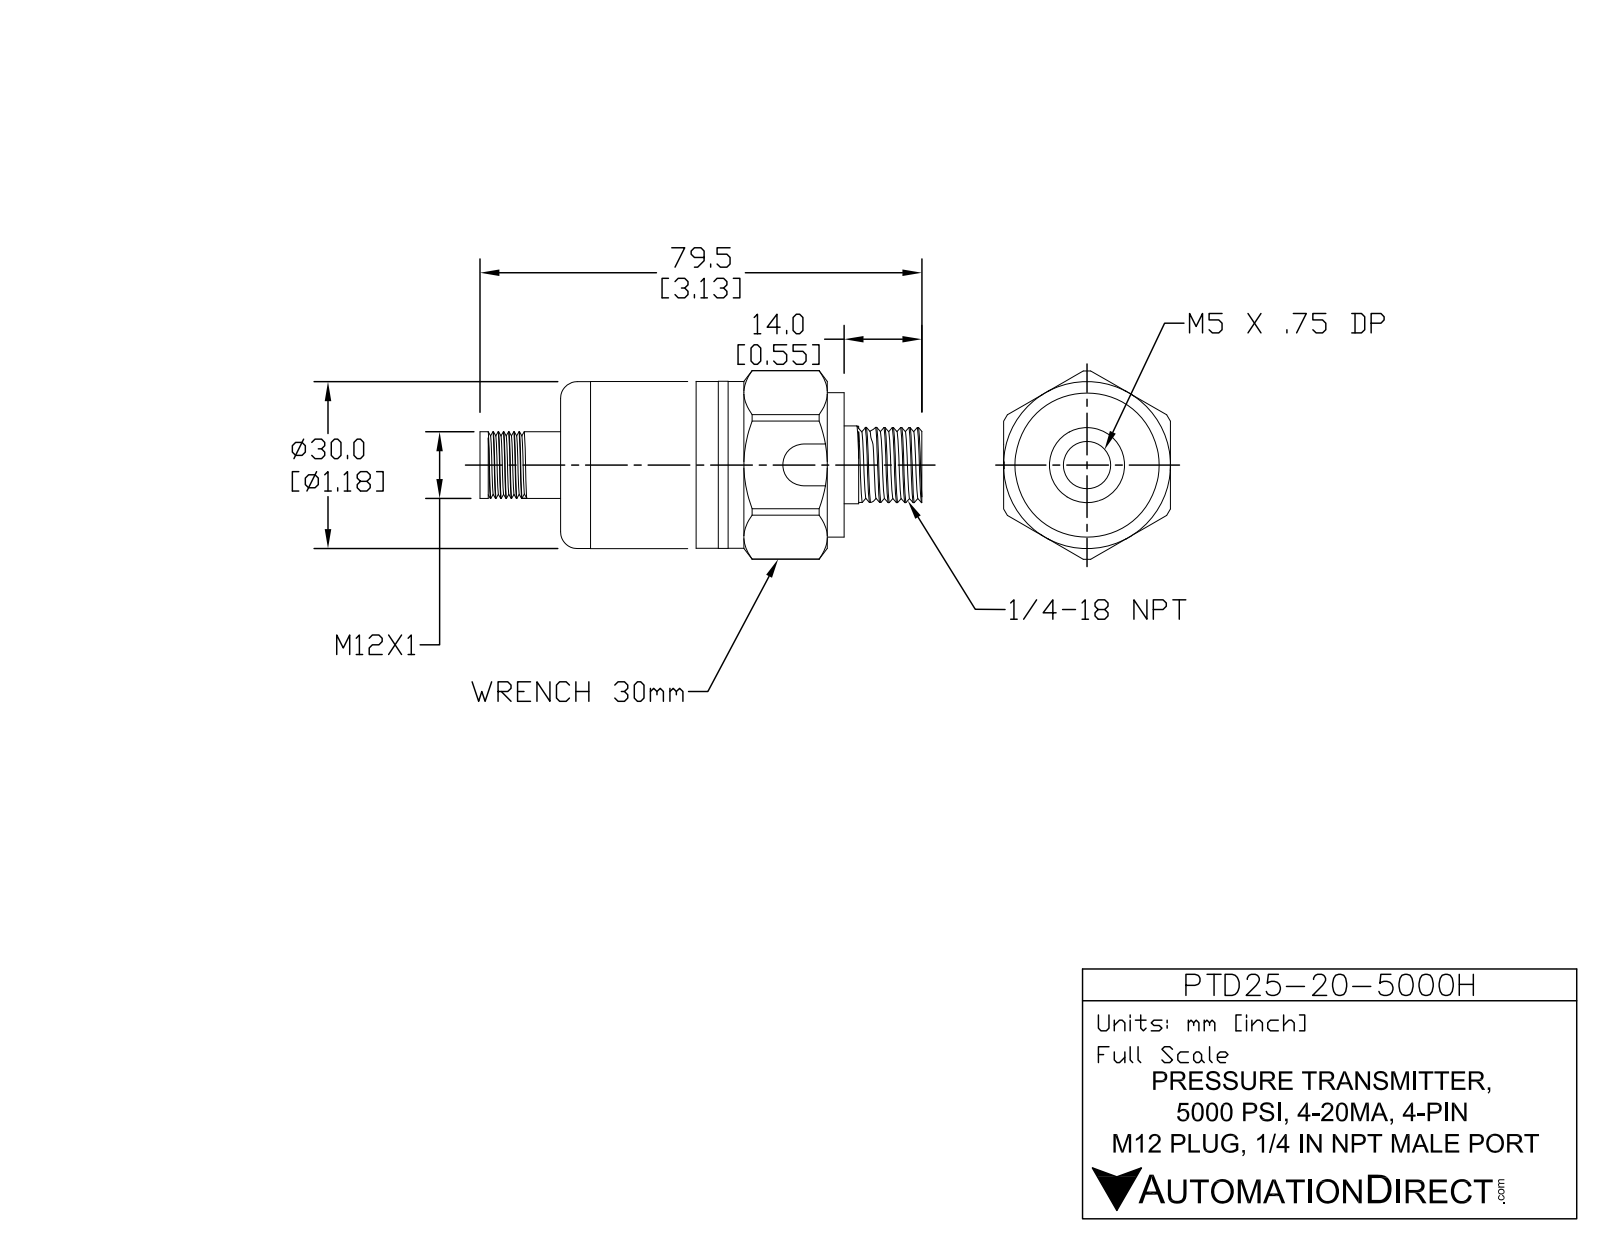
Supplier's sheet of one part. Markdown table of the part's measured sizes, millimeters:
| quantity | value |
| --- | --- |
| part name | PTD25-20-5000H |
| STEP written by | SolidWorks 2017 (AUTOMOTIVE_DESIGN) |
| units | millimeters |
| bodies | 1 solid, 124 faces (36 planar, 59 cylindrical, 29 other) |
| overall size | 79.5 × 33.78 × 31.7 |
| volume | 39 212 mm³ |
| surface area | 8 088 mm² |
| round holes (diameter × count) | 4 × 1, 8.5 × 1 |
| round bosses / shafts (diameter × count) | 30.05 × 1, 30 × 1, 25.96 × 1, 14 × 1, 13.5 × 1, 12 × 1 |
| partial cylindrical surfaces (radius × count) | 3.76 × 1, 16.95 × 1 |
| main face-to-face distances | 51, 29.98, 30, 48, 3, 65, 17, 14, 30.01, 5.65 |
